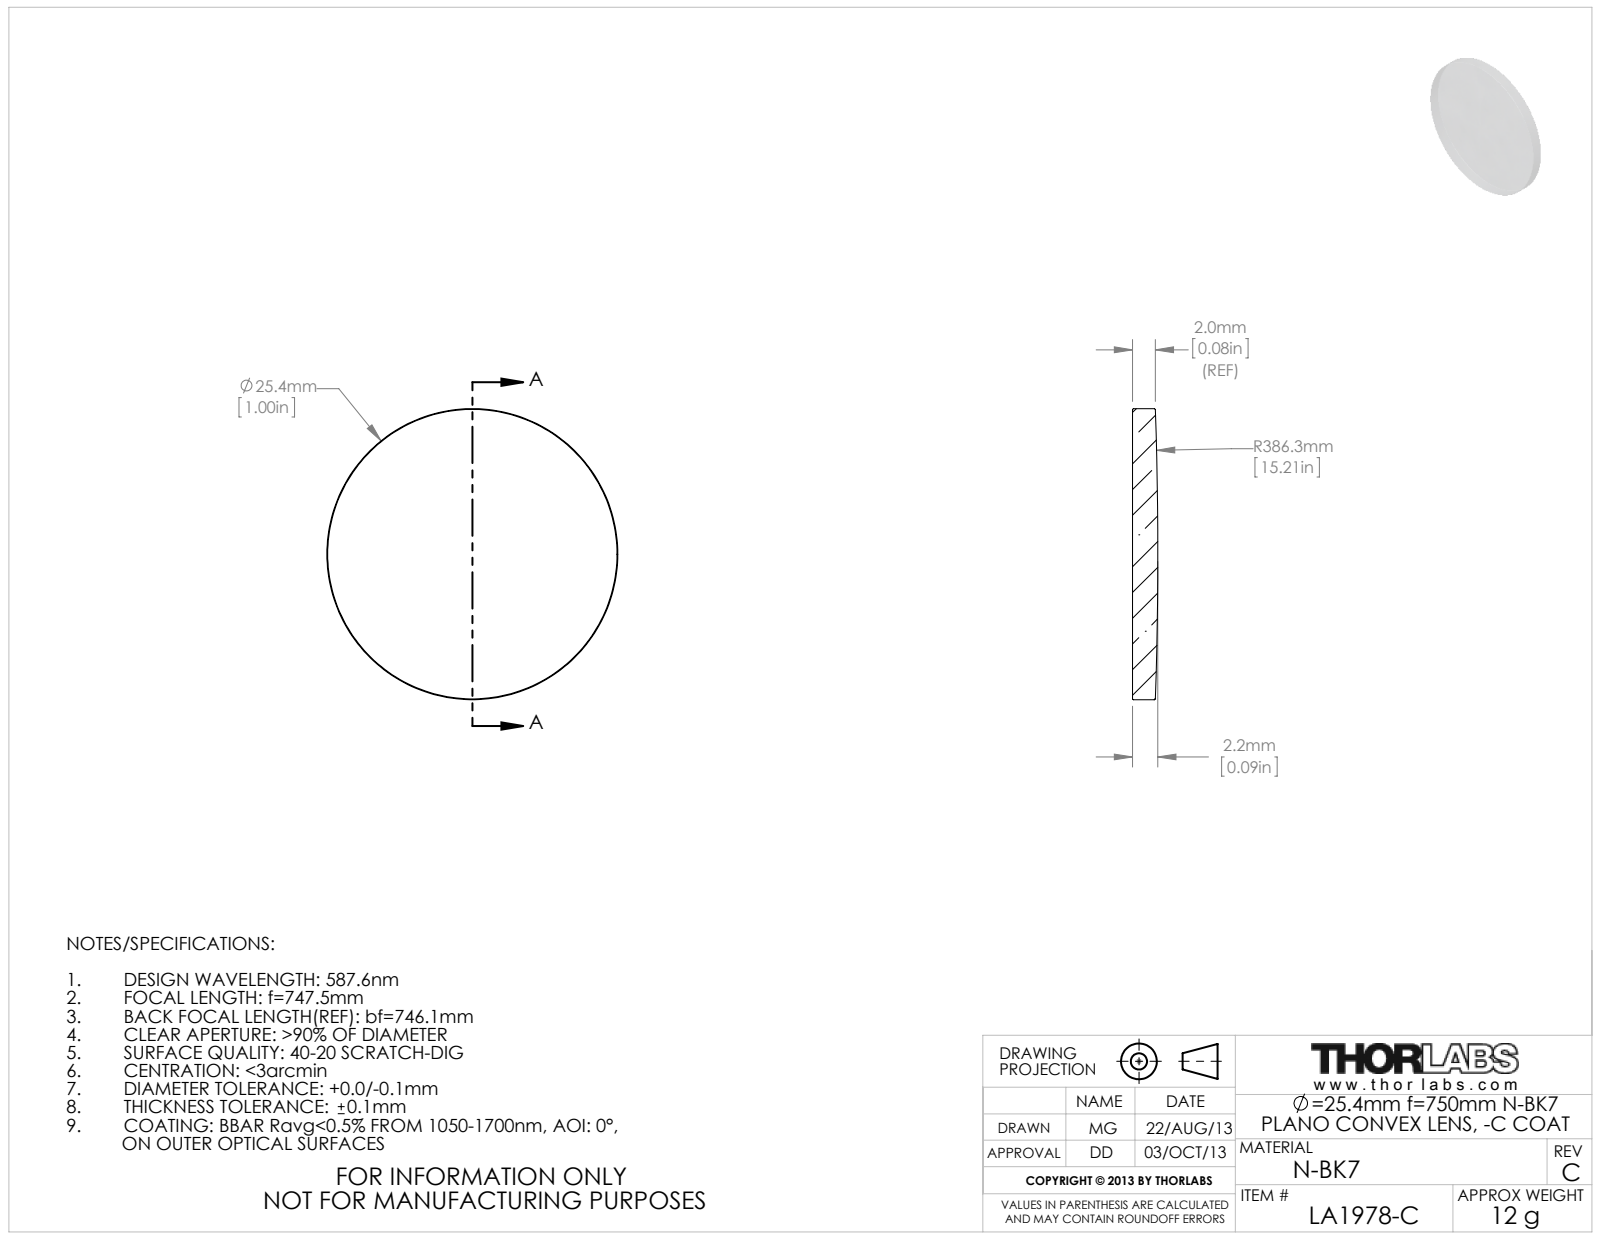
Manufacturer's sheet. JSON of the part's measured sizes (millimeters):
{"part_name": "4593-E0W", "step_written_by": "SolidWorks 2009 (AUTOMOTIVE_DESIGN)", "units": "millimeters", "bodies": {"solids": 1, "faces": 5, "planar": 1, "cylindrical": 2, "other": 2}, "overall_size": [25.4, 25.4, 2.2], "volume_mm3": 1062, "surface_area_mm2": 1172, "round_bosses_or_shafts": [[25.4, 1]]}
